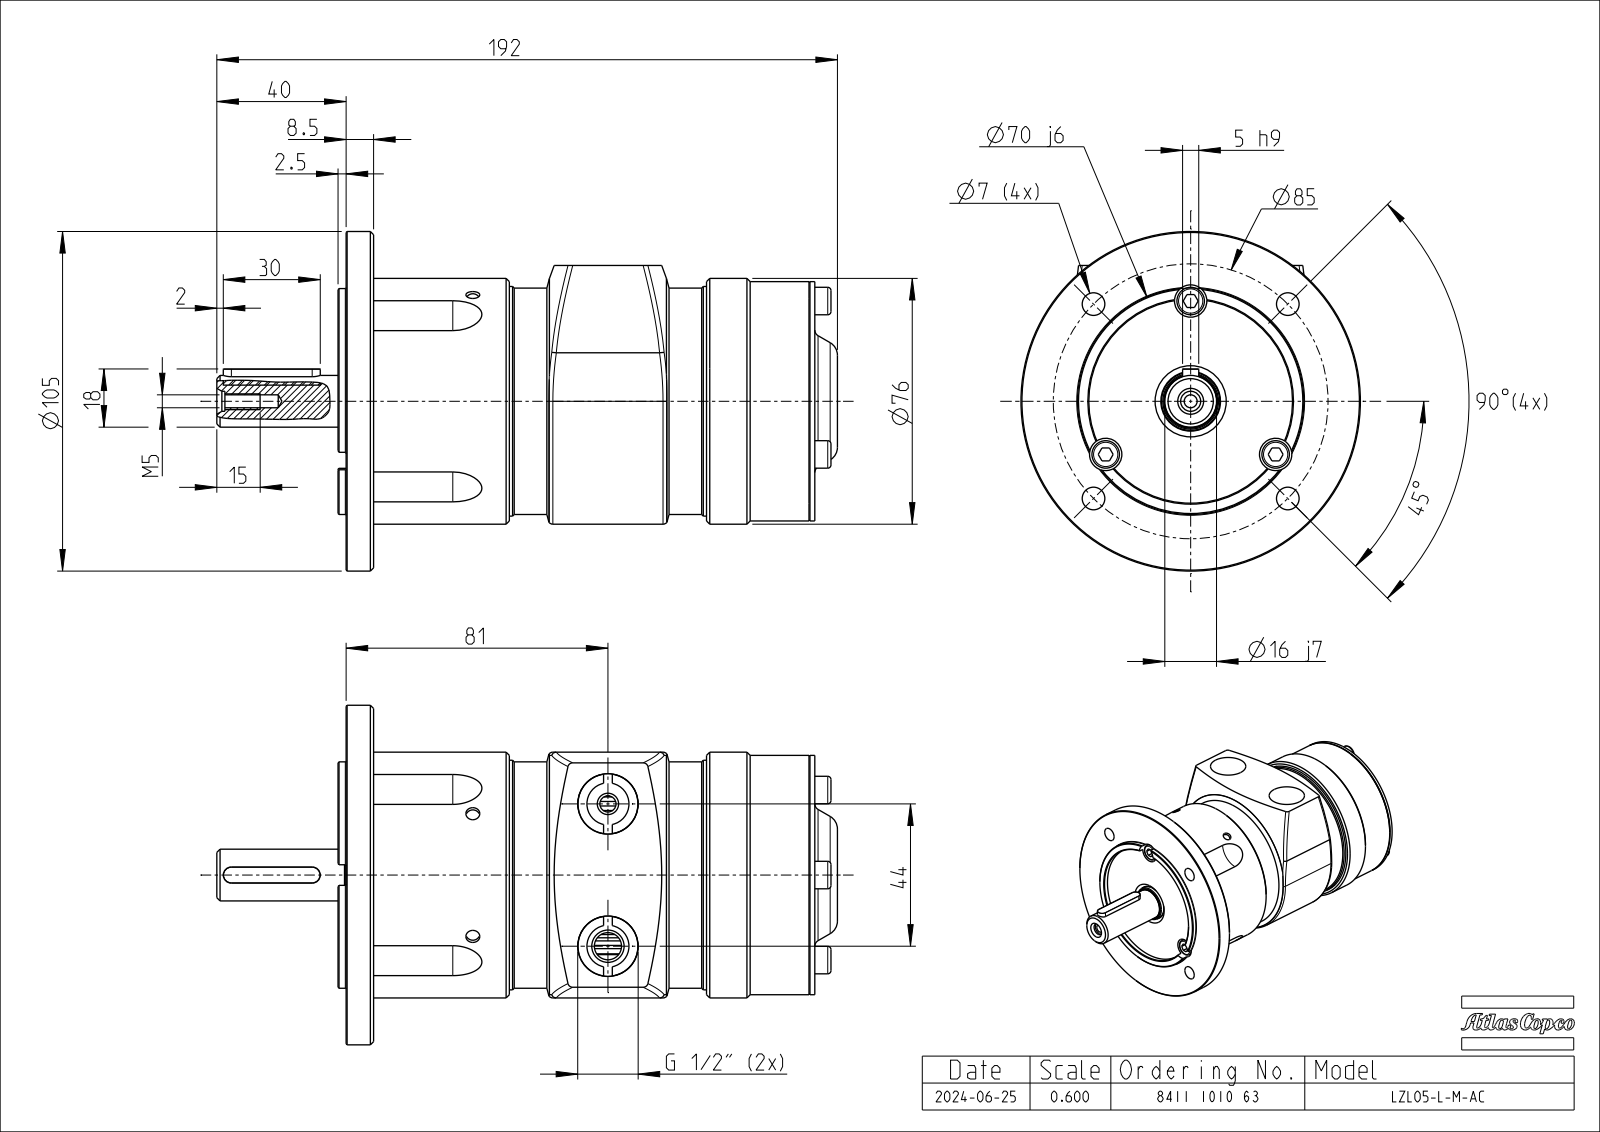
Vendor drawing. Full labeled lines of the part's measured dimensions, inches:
Part name (STEP PRODUCT): 8411101030_SW0001
STEP written by: CREO PARAMETRIC BY PTC INC, 2022414 (AP242_MANAGED_MODEL_BASED_3D_ENGINEERING_MIM_LF)
Units: inches
Bodies: 3 solids, 351 faces (105 planar, 121 cylindrical, 125 other)
Overall size (bounding box): 7.559 × 4.134 × 4.134
Volume: 42.77 in³ · Surface area: 106.7 in²
Round holes (diameter × count): ⌀0.276 ×5, ⌀0.169 ×4, ⌀0.157 ×3, ⌀0.394 ×3, ⌀0.177 ×2, ⌀0.315 ×2, ⌀0.736 ×2, ⌀0.244 ×1, ⌀0.512 ×1, ⌀0.531 ×1, ⌀0.866 ×1, ⌀2.48 ×1
Round bosses / shafts (diameter × count): ⌀0.335 ×3, ⌀0.236 ×2, ⌀4.134 ×1, ⌀2.992 ×1, ⌀2.913 ×1, ⌀2.795 ×1, ⌀2.756 ×1, ⌀0.709 ×1
Partial cylindrical surfaces — rounded edges, fillets, slot ends (radius × count): R0.004 ×4, R0.394 ×4, R0.118 ×2, R0.412 ×2
Main face-to-face distances: 0.335, 5.374, 5.709, 0.276, 5.65, 0.098, 5.807, 5.984, 0.433, 6.083
Hole centre spacings: 1.673, 2.366, 0.693, 1.181, 1.22, 0.488, 0.556, 0.614
